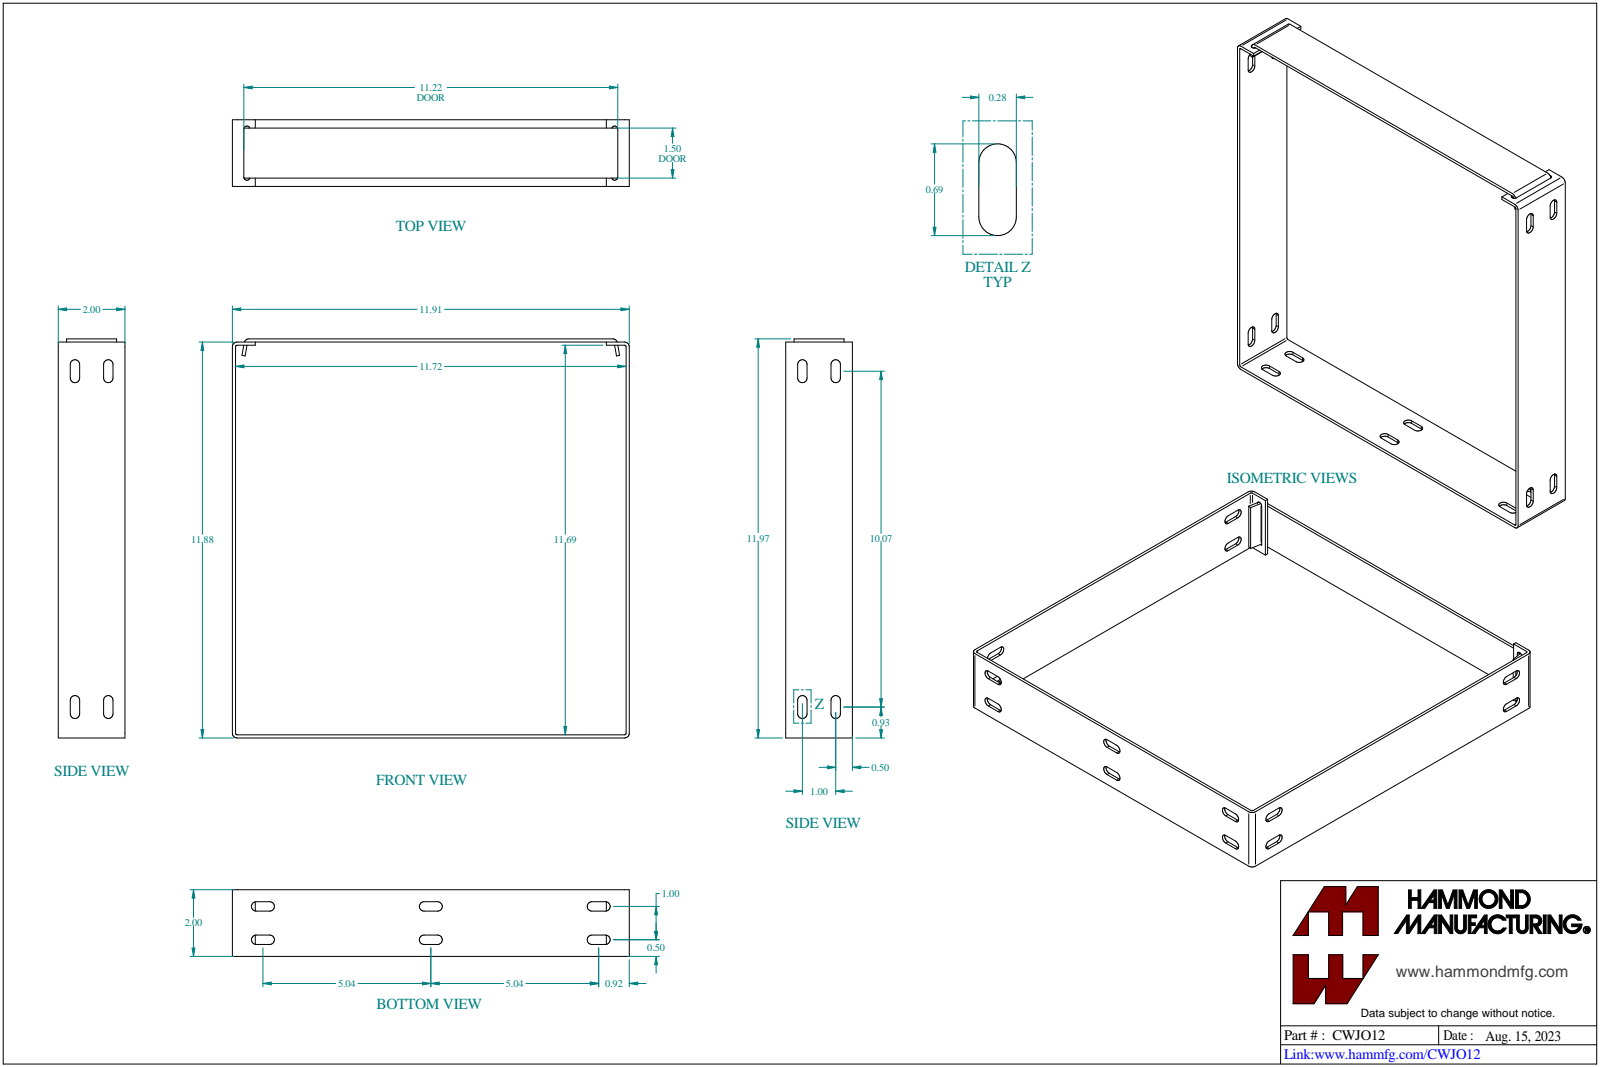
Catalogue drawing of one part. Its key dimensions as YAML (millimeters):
part_name: "CWJO12"
step_written_by: "SolidWorks 2023 (CONFIG_CONTROL_DESIGN)"
units: millimeters
bodies: {solids: 2, faces: 114, planar: 56, cylindrical: 58, other: 0}
overall_size: [304, 302.4, 50.8]
volume: 136700
surface_area: 121500
partial_cylinders:
  - {radius: 3.6, count: 12}
  - {radius: 3.6, count: 8}
  - {radius: 1.2, count: 6}
  - {radius: 3.6, count: 6}
  - {radius: 2.4, count: 4}
face_to_face_distances: [2.4, 300, 2.4, 297.6, 302.4, 299.2, 301.6, 304, 301.6, 50.8]
